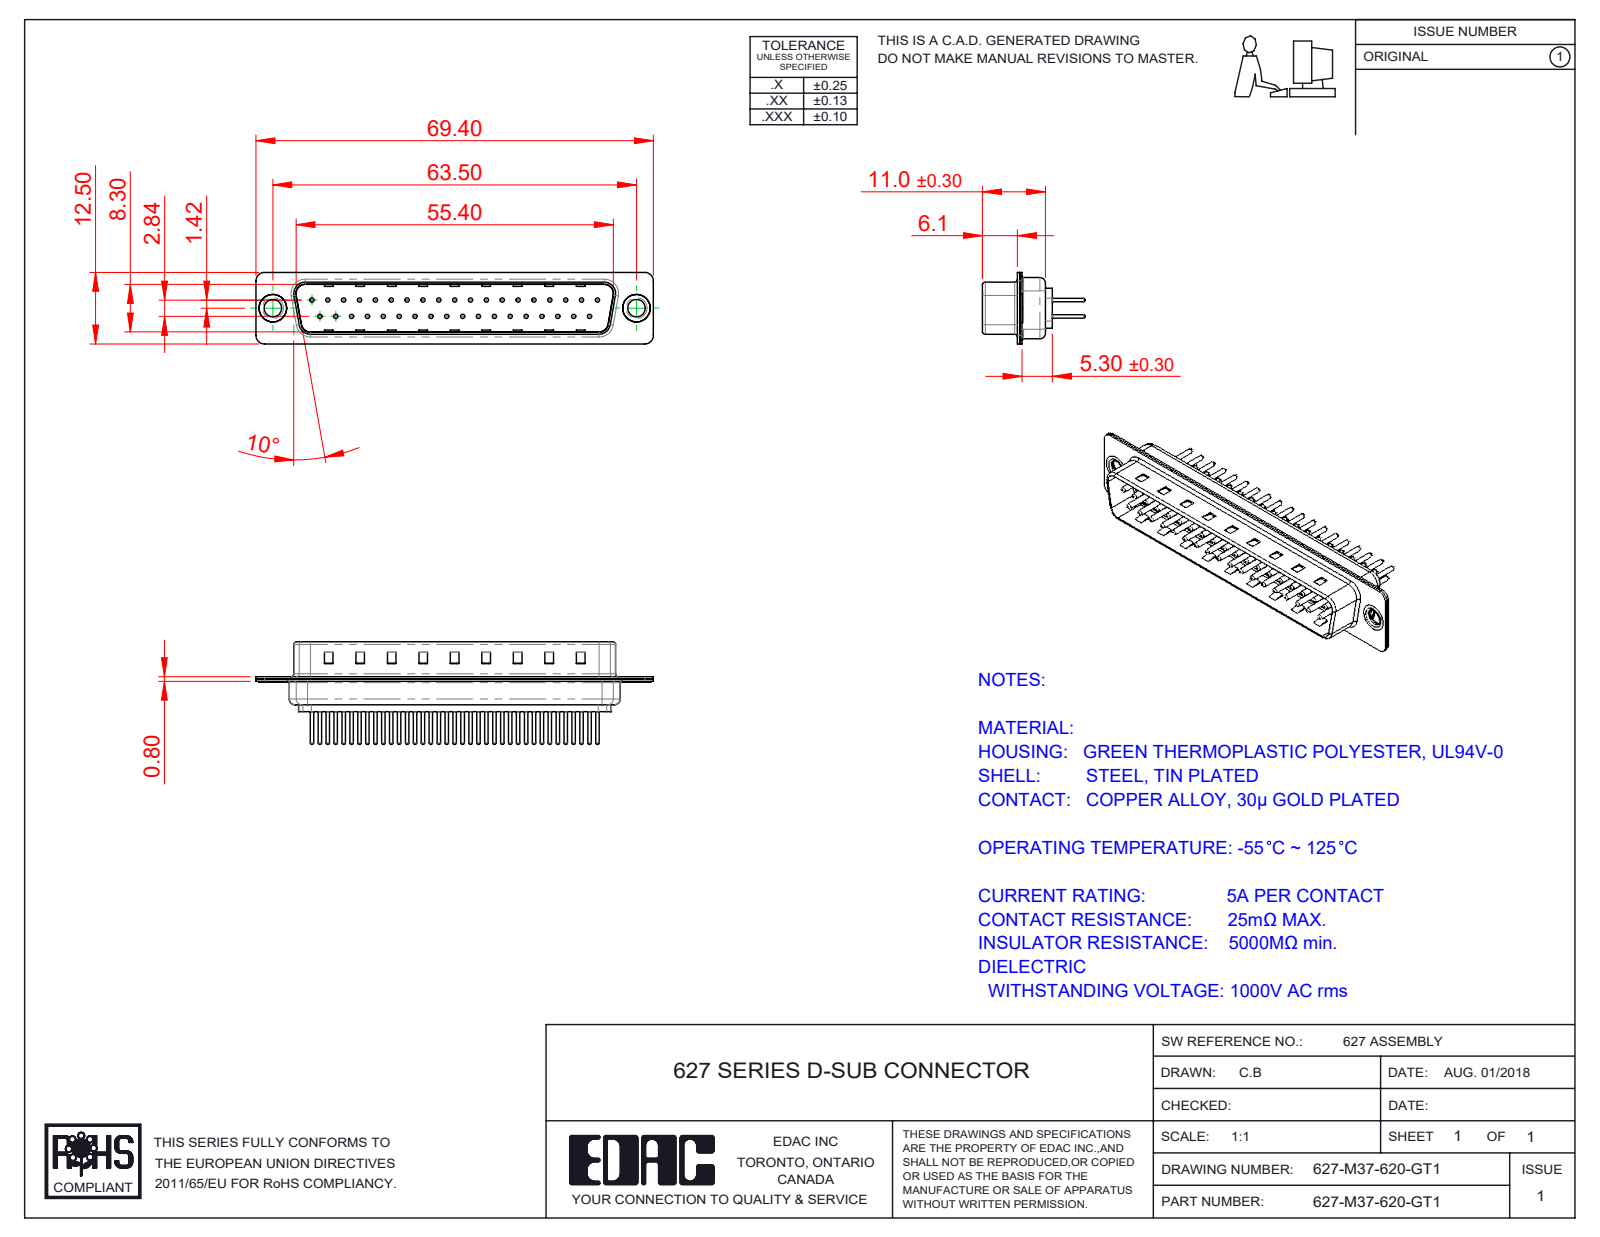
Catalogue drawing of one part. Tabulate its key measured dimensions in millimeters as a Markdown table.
| quantity | value |
| --- | --- |
| part name | 627M Thru Hole Rivet; 627M Housing_37 Contacts; 627-M37-620-GT1; 627M Contact Row 1_20 (+3 more) |
| STEP written by | SolidWorks 2020 (CONFIG_CONTROL_DESIGN) |
| units | millimeters |
| bodies | 42 solids, 1755 faces (462 planar, 643 cylindrical, 650 other) |
| overall size | 69.4 × 17.9 × 12.5 |
| volume | 3 690 mm³ |
| surface area | 9 124 mm² |
| round holes (diameter × count) | 0.75 × 37, 1.6 × 37, 2 × 37, 3.05 × 2, 4 × 2, 4.8 × 2 |
| round bosses / shafts (diameter × count) | 1.5 × 37, 0.6 × 37, 5 × 2, 4.9 × 2, 3.55 × 2 |
| partial cylindrical surfaces (radius × count) | 1.5 × 16, 2 × 12, 0.5 × 8, 1.6 × 8, 0.25 × 4, 0.6 × 4, 0.65 × 4, 0.9 × 4 |
| main face-to-face distances | 0.4, 0.8, 9.5, 9.1, 8.7, 9.9, 1.2, 5.7, 0.75, 0.35 |
| hole center spacings | 2.77, 5.54, 3.16, 8.31, 11.08, 13.85, 16.62, 19.39 |
